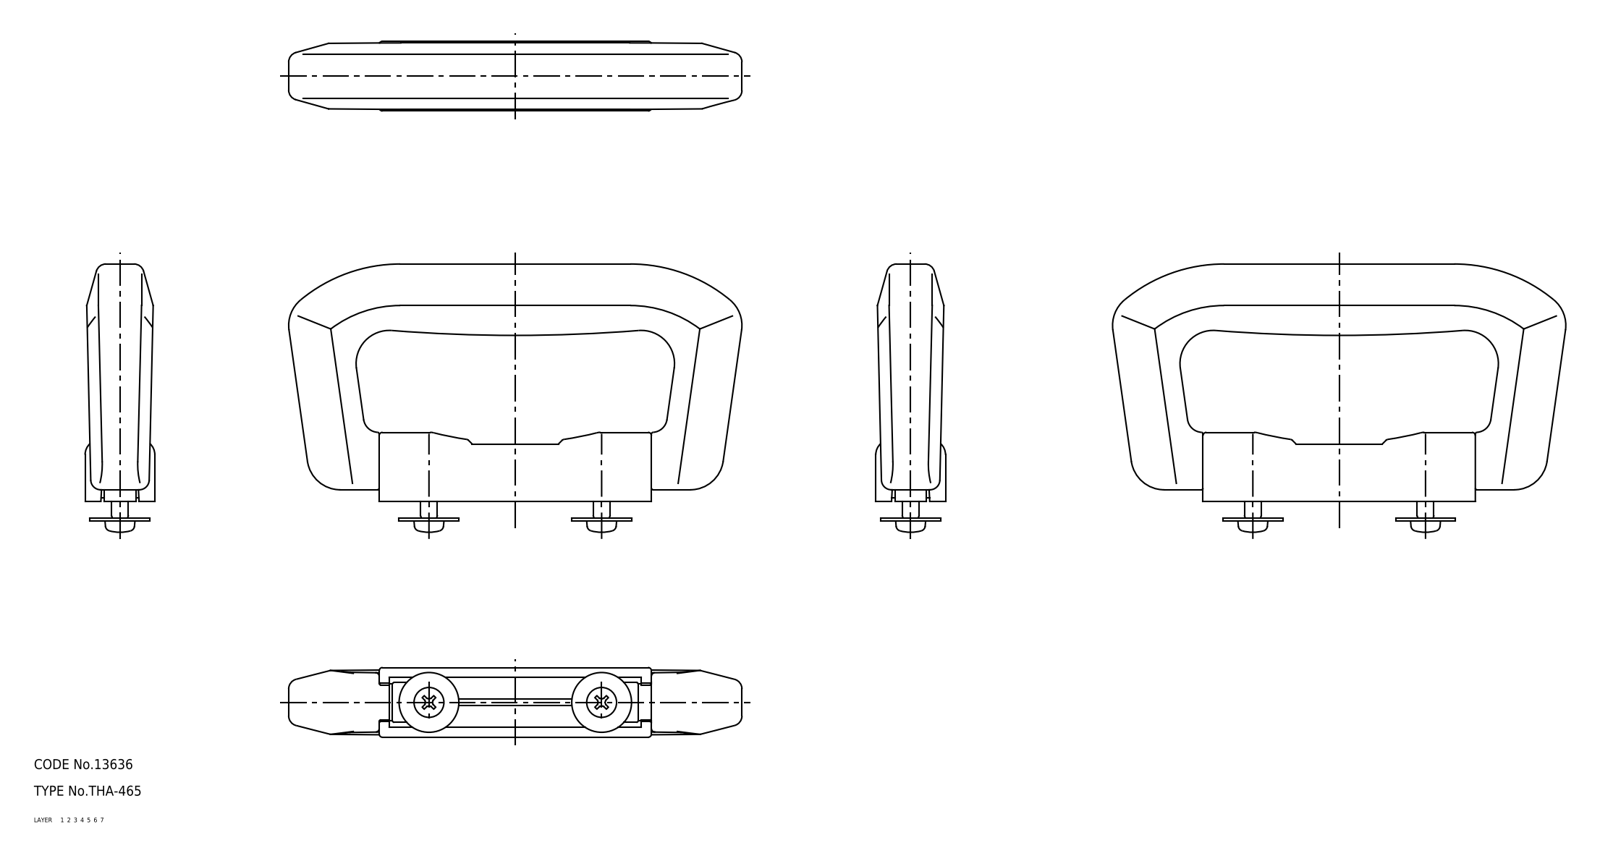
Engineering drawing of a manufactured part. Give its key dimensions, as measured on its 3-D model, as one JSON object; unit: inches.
{"part_name": "grip; base; screw; THA-465", "step_written_by": "SolidWorks 2015 (AUTOMOTIVE_DESIGN)", "units": "inches", "bodies": {"solids": 4, "faces": 200, "planar": 69, "cylindrical": 42, "other": 89}, "overall_size": [5.374, 3.181, 0.827], "volume_in3": 5.234, "surface_area_in2": 44.56, "round_holes": [[0.165, 2]], "round_bosses_or_shafts": [[0.709, 2], [0.374, 2], [0.197, 2], [0.472, 1], [0.433, 1]], "partial_cylinders_radius": [[0.039, 8], [0.22, 1]], "face_to_face_distances": [0.118, 0.709, 0.374, 0.453, 0.256, 0.335, 0.827, 0.591, 0.079, 0.236], "hole_center_spacings": [2.047]}
